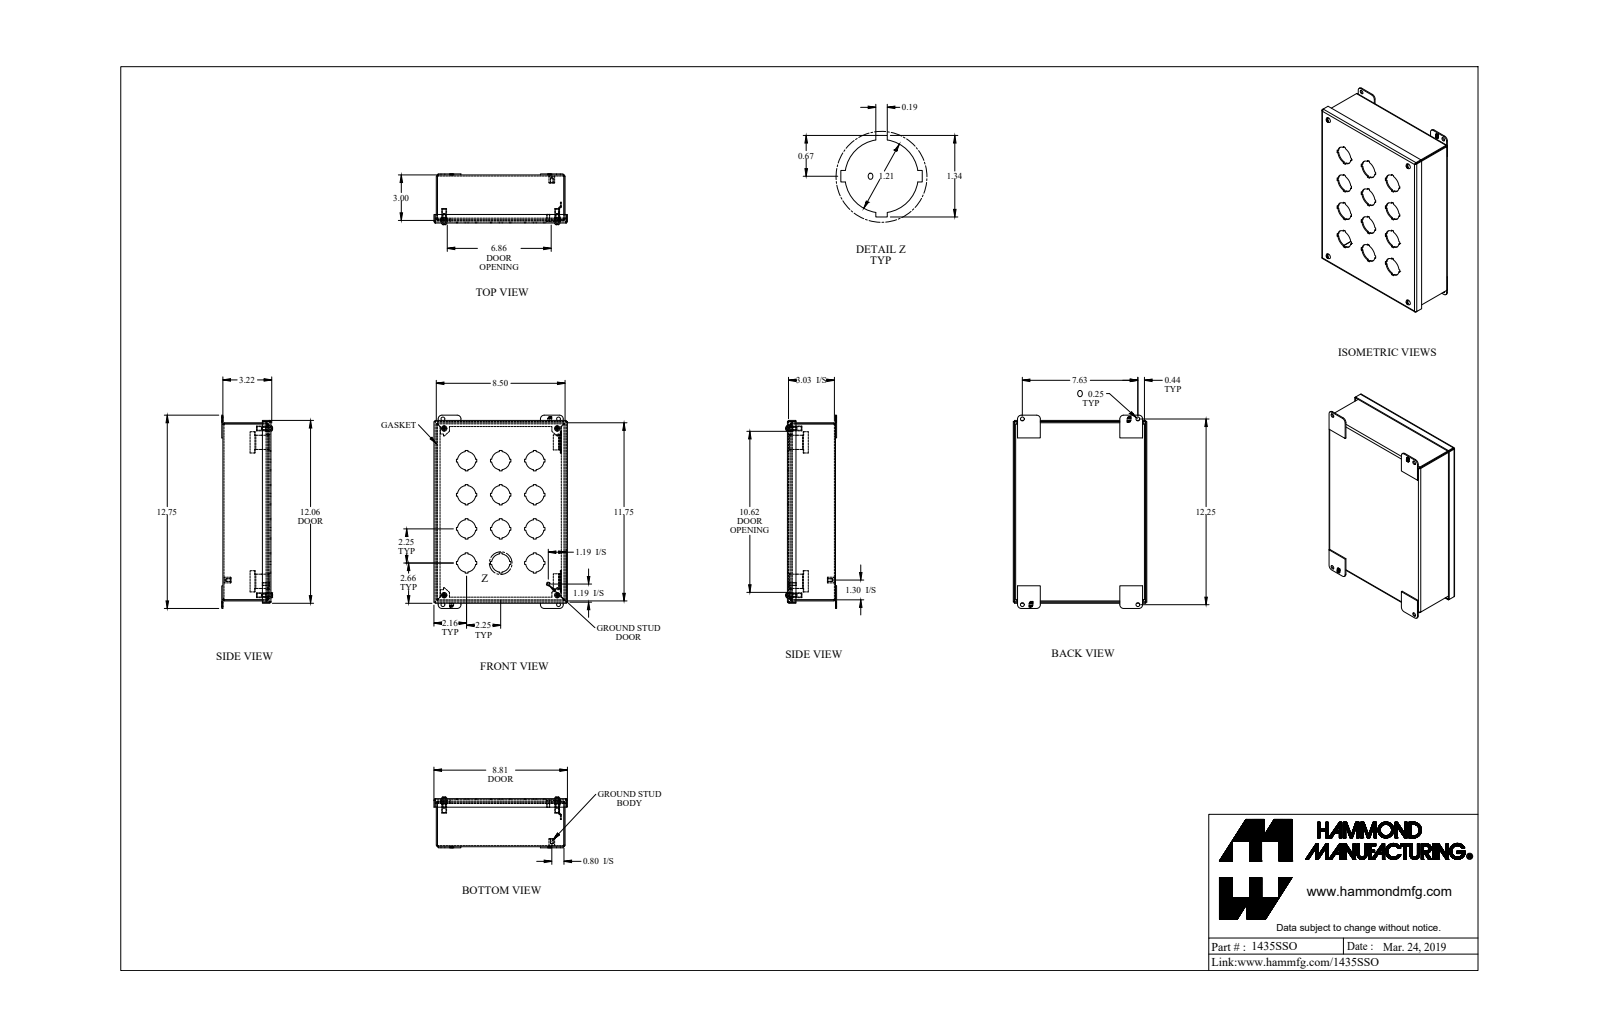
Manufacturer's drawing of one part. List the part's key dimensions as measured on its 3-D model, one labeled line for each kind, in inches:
Part name (STEP PRODUCT): 1435SSO_Default
STEP written by: SolidWorks 2019 (CONFIG_CONTROL_DESIGN)
Units: inches
Bodies: 23 solids, 797 faces (567 planar, 200 cylindrical, 30 other)
Overall size (bounding box): 12.75 × 8.81 × 3.354
Volume: 28.91 in³ · Surface area: 768.3 in²
Round holes (diameter × count): ⌀1.21 ×12, ⌀0.25 ×8, ⌀0.065 ×4, ⌀0.239 ×4, ⌀0.253 ×4, ⌀0.406 ×4, ⌀0.156 ×1
Round bosses / shafts (diameter × count): ⌀0.19 ×5, ⌀0.406 ×4, ⌀0.315 ×4, ⌀0.148 ×4, ⌀0.375 ×1, ⌀0.25 ×1
Partial cylindrical surfaces — rounded edges, fillets, slot ends (radius × count): R0.036 ×12, R0.108 ×12, R0.25 ×8, R0.029 ×4, R0.086 ×4, R0.171 ×4
Main face-to-face distances: 0.072, 3.1, 3.172, 3.028, 8.428, 0.072, 11.678, 8.5, 8.356, 0.155
Hole centre spacings: 2.25, 5.031, 3.182, 4.5, 7.46, 7.461, 7.569, 10.999
